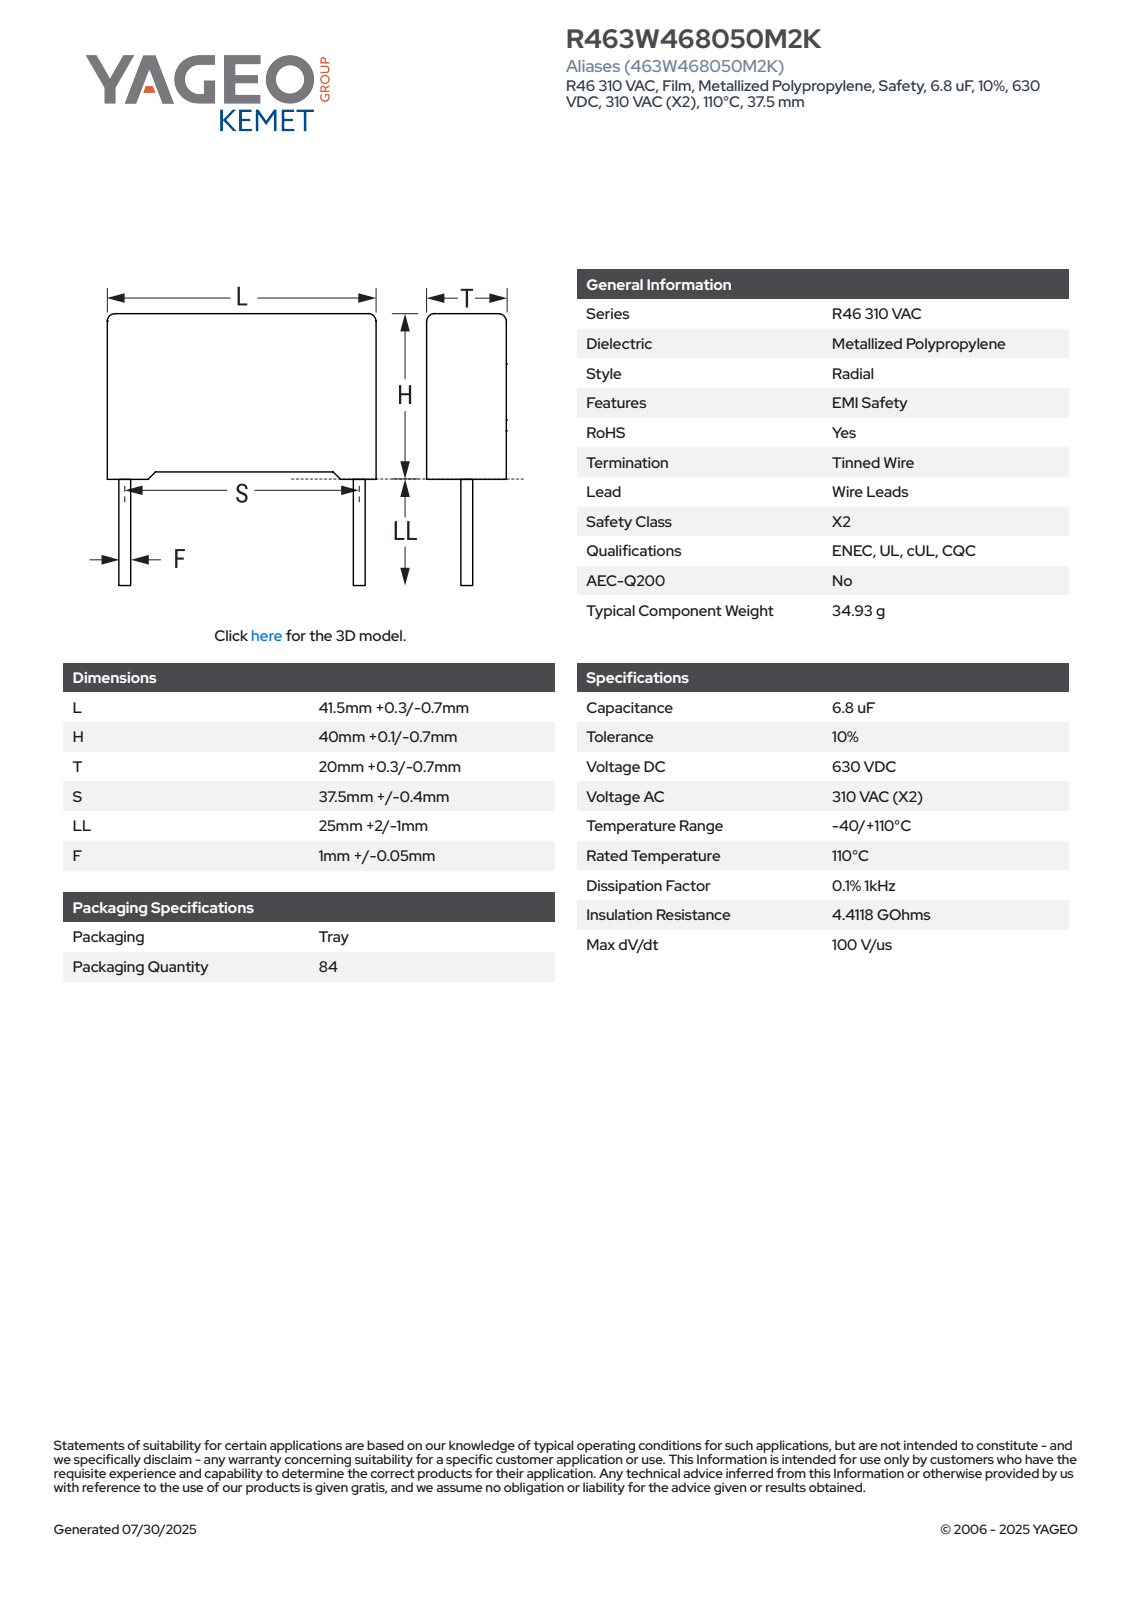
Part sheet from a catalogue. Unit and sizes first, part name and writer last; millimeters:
Units: millimetres
Overall size (bounding box): 67.1 × 41.8 × 20.3
Round bosses / shafts (diameter × count): ⌀1.05 ×2
Partial cylindrical surfaces — rounded edges, fillets, slot ends (radius × count): R0.5 ×4
Main face-to-face distances: 20.3, 41.8, 38.72, 0.63, 39.35, 0.75, 1.38, 40.1, 1.39, 20.31
Volume: 33 065 mm³ · Surface area: 6 920 mm²
Bodies: 4 solids, 85 faces (77 planar, 8 cylindrical, 0 other)
Part name (STEP PRODUCT): CFR_RB2_41.5X40X20_L41.8H40.1T20.3S37.5LL27F1.05
STEP written by: SolidWorks 2021 (AUTOMOTIVE_DESIGN)
